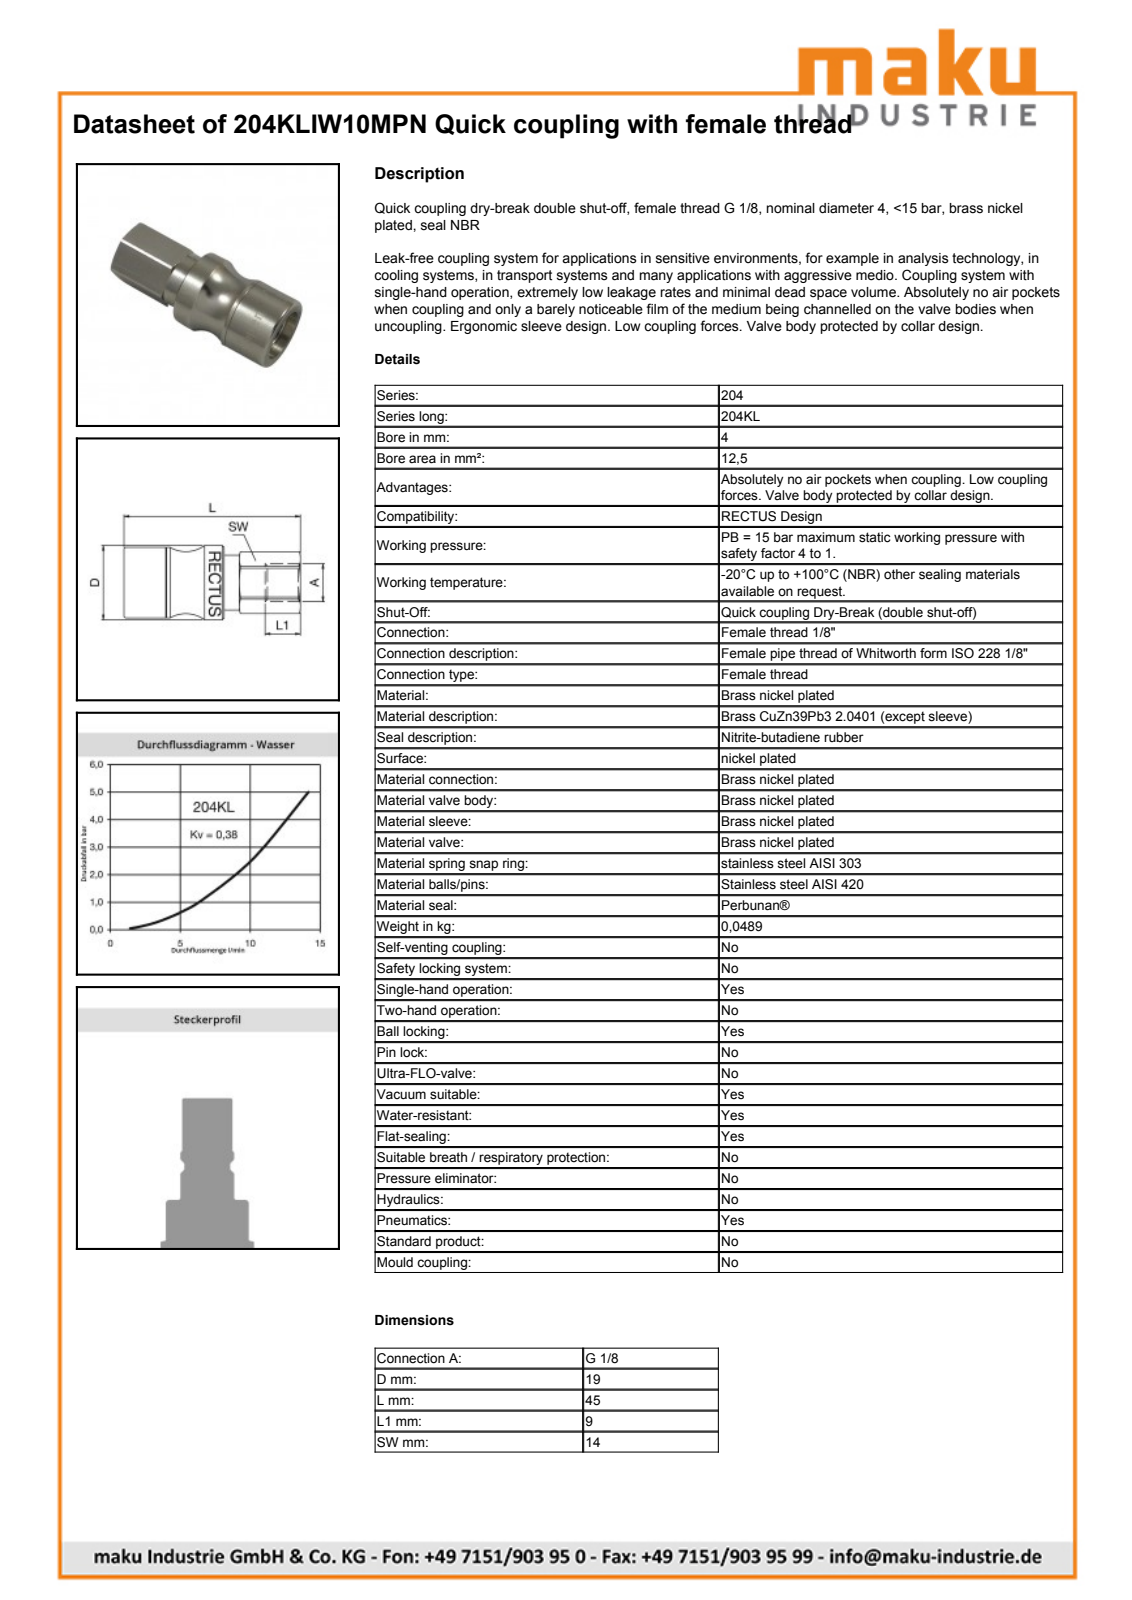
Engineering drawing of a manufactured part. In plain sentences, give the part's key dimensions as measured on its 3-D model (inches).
The part is named "D108102". Its 3-D file was written by "Autodesk Inventor 2013 (AUTOMOTIVE_DESIGN)". It is 1 solid with 47 faces: 11 planar, 13 cylindrical and 23 other. Overall it measures 1.571 by 0.622 by 0.551 inches. Its volume is 0.245 cubic inches and its surface area 2.652 square inches. Round bosses or shafts: 1 of diameter 0.551, 1 of diameter 0.383, 1 of diameter 0.354, 1 of diameter 0.331, 1 of diameter 0.299. Partial cylindrical surfaces (rounded edges, fillets, slot ends): 1 of radius 0.311. The main face-to-face distances are 0.551, 0.276, 0.606, 0.882, 0.689, 1.295, 1.571, 0.783, 0.094, 0.512.
